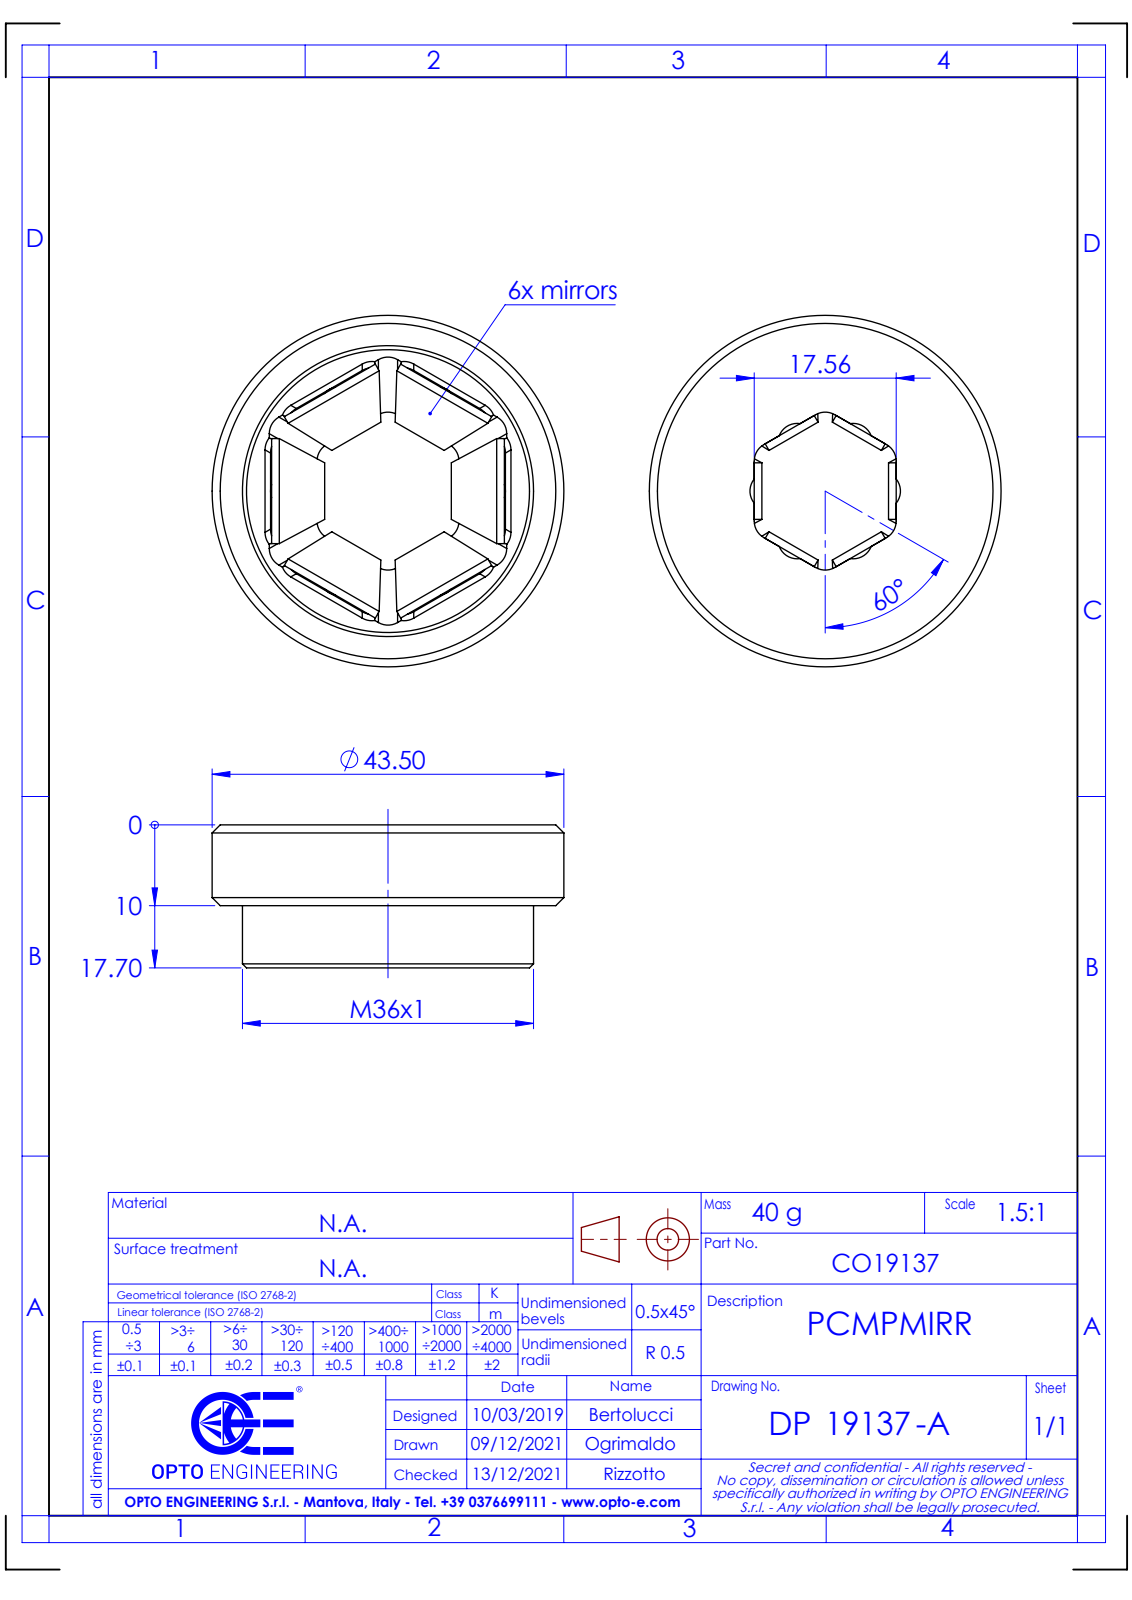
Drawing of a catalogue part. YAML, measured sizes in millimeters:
part_name: "DP19137-A_PCMPMIRR"
step_written_by: "SolidWorks 2021 (CONFIG_CONTROL_DESIGN)"
units: millimeters
bodies: {solids: 0, faces: 105, planar: 65, cylindrical: 34, other: 6}
overall_size: [43.5, 43.5, 17.7]
round_bosses_or_shafts:
  - {diameter: 43.5, count: 1}
  - {diameter: 36, count: 1}
partial_cylinders:
  - {radius: 2.5, count: 24}
face_to_face_distances: [1, 10, 1.01, 17.7, 7.7, 1.5, 0.5, 0.49, 17.75, 16.66]
